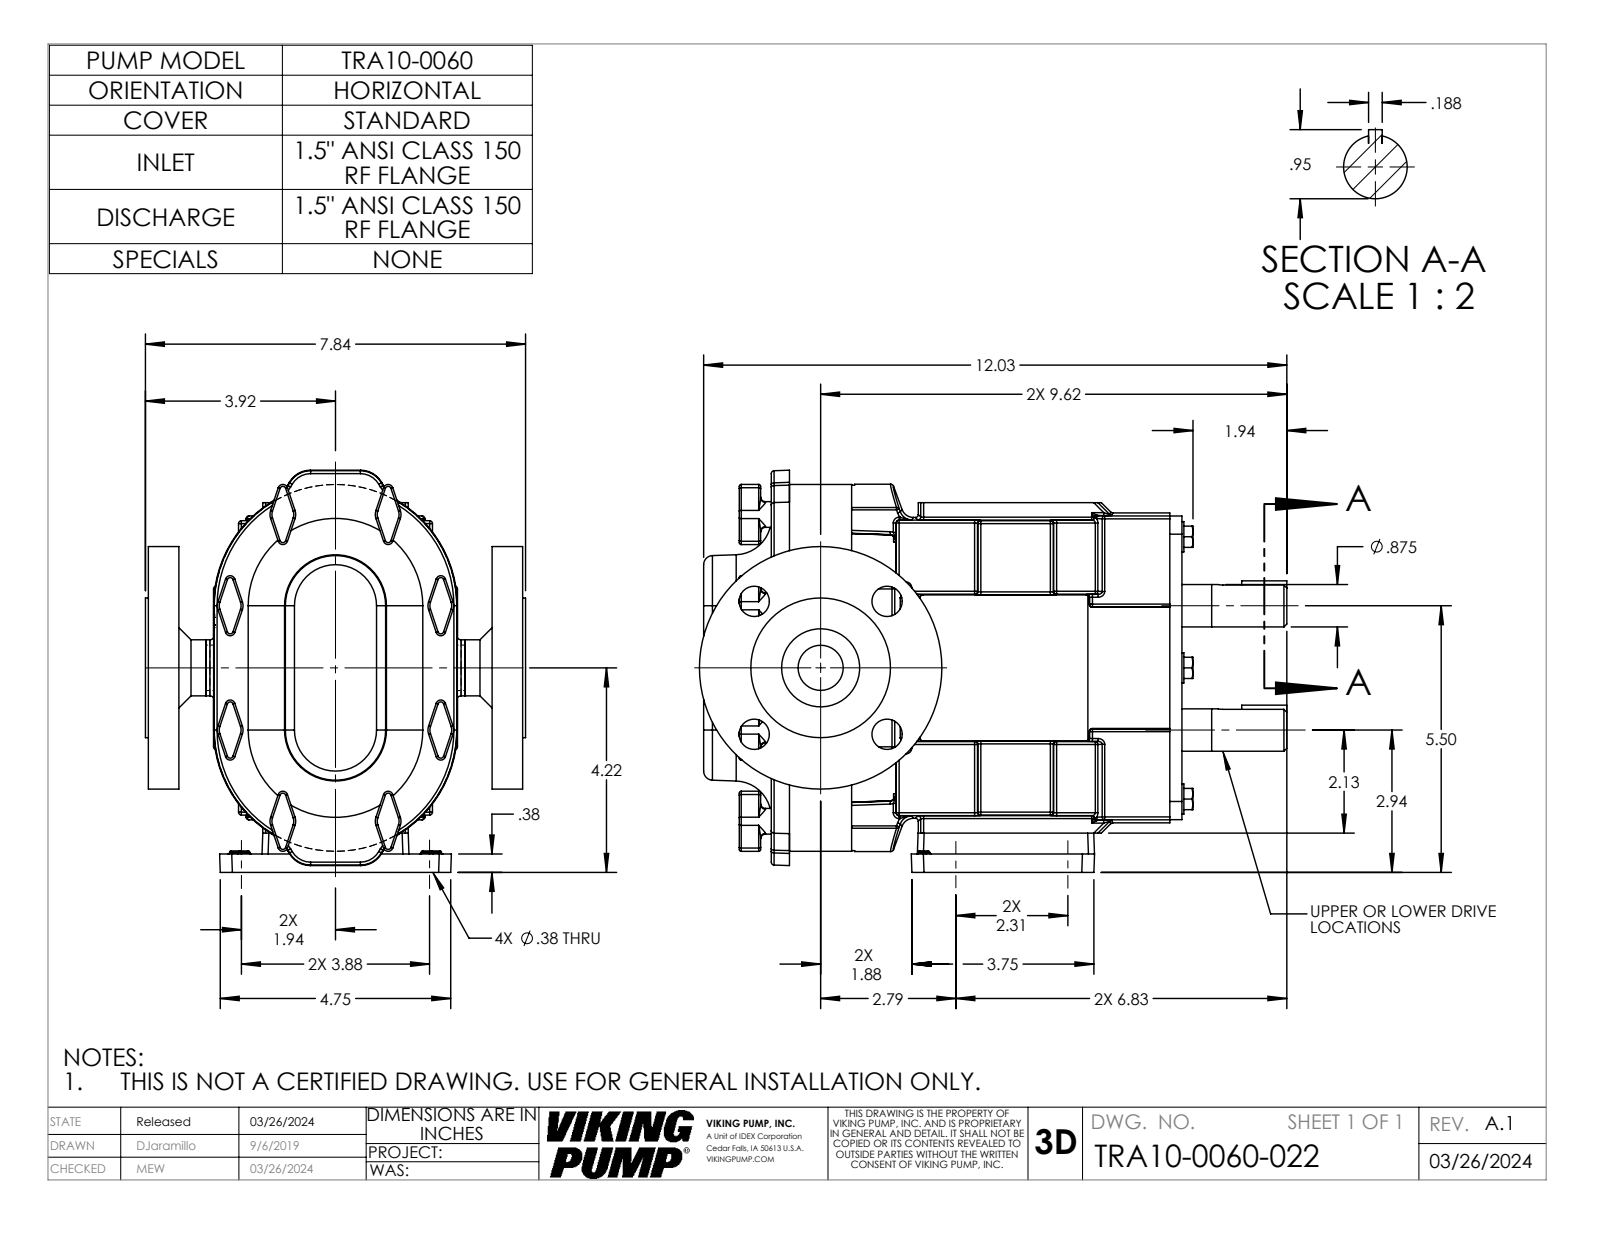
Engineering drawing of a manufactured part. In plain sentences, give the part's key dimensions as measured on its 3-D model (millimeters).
The part is named "0150FLG150-15; TRA10-0150-COVER-STD; TRA10-0060-022; TRA10-0150-GEARBOX-H (+1 more)". Its 3-D file was written by "SolidWorks 2022 (AUTOMOTIVE_DESIGN)". It is 5 solids with 1203 faces: 321 planar, 469 cylindrical and 413 other. Overall it measures 307.7 by 210.6 by 199.1 millimeters. Its volume is 4 187 000 cubic millimeters and its surface area 372 300 square millimeters. Round holes: 4 of diameter 9.5, 4 of diameter 15.9, 1 of diameter 23.6, 1 of diameter 23.8, 1 of diameter 40.9. Round bosses or shafts: 8 of diameter 13.5, 6 of diameter 15.9, 2 of diameter 22.2, 1 of diameter 127, 1 of diameter 73.2, 1 of diameter 29.4. Partial cylindrical surfaces (rounded edges, fillets, slot ends): 189 of radius 1.5, 64 of radius 1, 20 of radius 3.2, 16 of radius 0.8, 16 of radius 2.5, 14 of radius 6.4, 4 of radius 9.5, 4 of radius 12.7. The main face-to-face distances are 32.6, 16, 180.1, 44.1, 152, 28.1, 136, 205.6, 173.1, 164.1. The hole center spacings are 49.2, 69.6, 58.7, 98.4, 98.6, 114.7.
